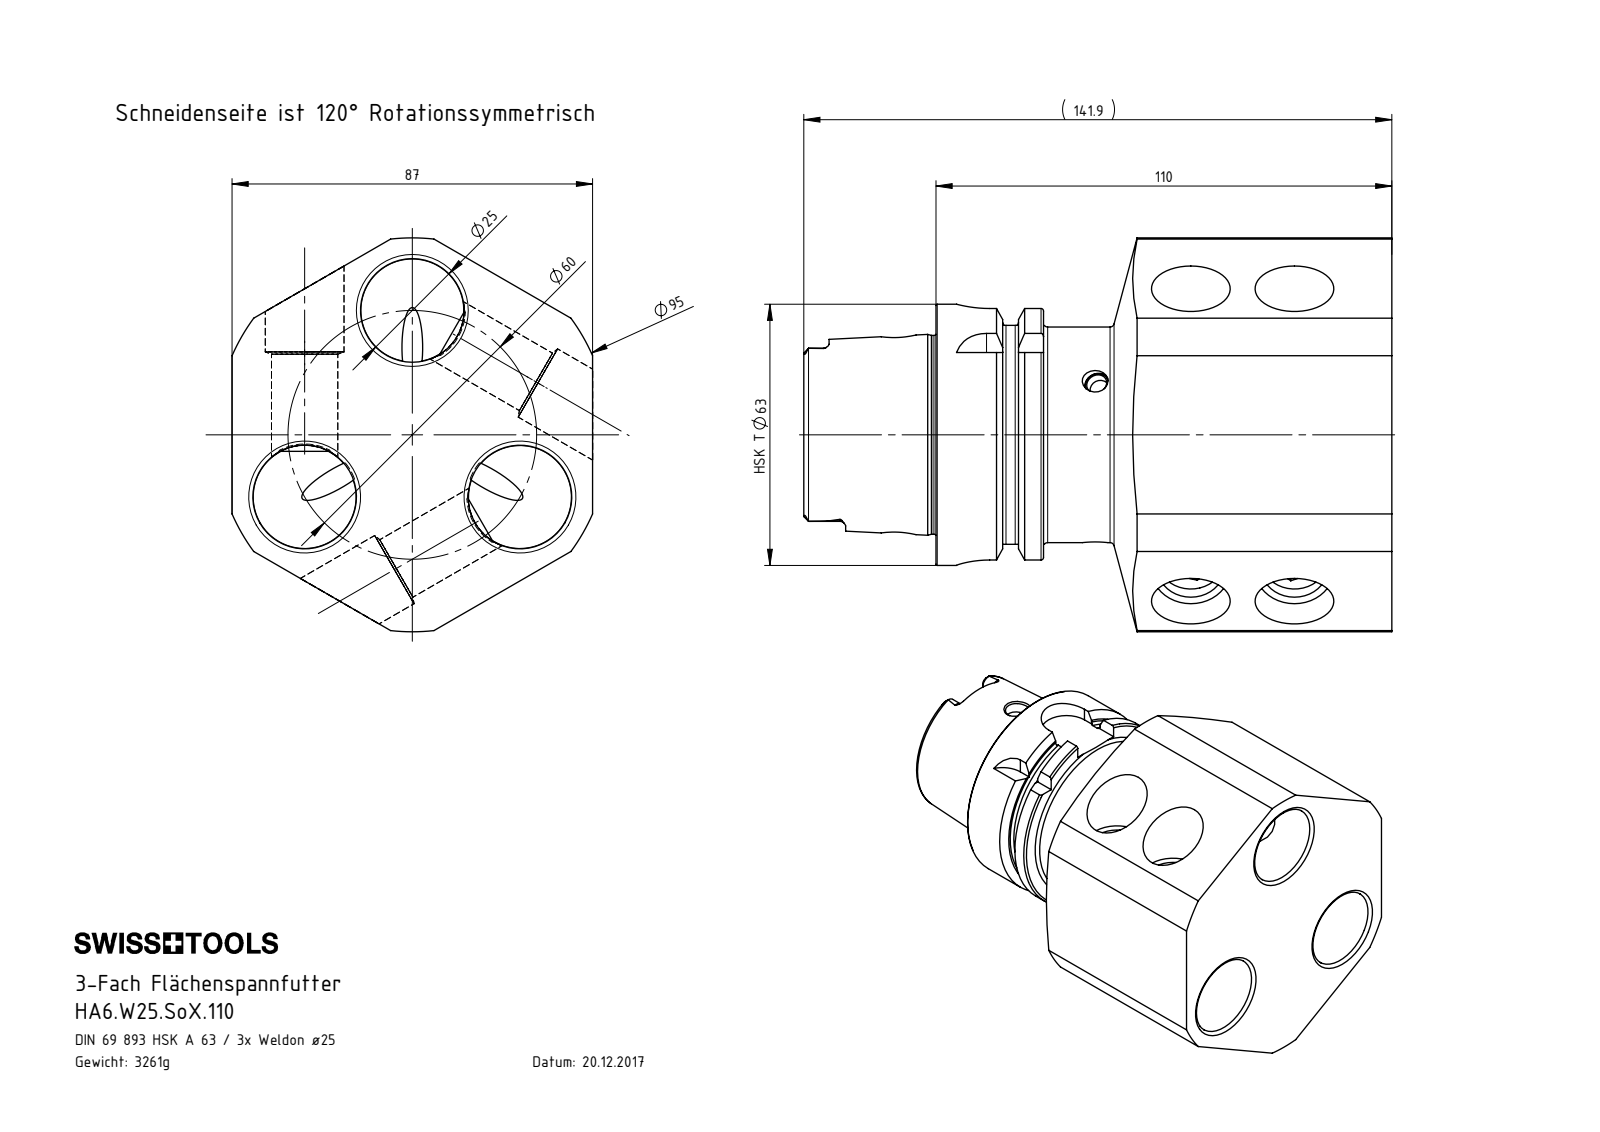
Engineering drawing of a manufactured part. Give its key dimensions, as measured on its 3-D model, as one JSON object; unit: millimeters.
{"part_name": "HA6-W25.SoX.110; W25-ER1.001.020; HA6-W25.SoX.110_A_Fertigbearbeitung; KVT_MB_600_060", "step_written_by": "SolidWorks 2017 (AUTOMOTIVE_DESIGN)", "units": "millimeters", "bodies": {"solids": 13, "faces": 529, "planar": 146, "cylindrical": 138, "other": 245}, "overall_size": [141.9, 95, 87], "volume_mm3": 415429, "surface_area_mm2": 90613, "round_holes": [[19, 7], [5, 6], [16, 6], [6, 3], [25, 3], [25.6, 3], [7.5, 1], [8.5, 1], [10, 1], [17, 1], [34, 1], [40, 1]], "round_bosses_or_shafts": [[18, 6], [6, 3], [63, 1], [54.95, 1], [52, 1], [47.94, 1]], "partial_cylinders_radius": [[1.4, 6], [2.88, 4], [8, 4], [47.5, 1]], "face_to_face_distances": [87, 59, 51, 110, 10, 25.95, 25.05, 84.05, 16, 9.95], "hole_center_spacings": [25, 30, 51.96, 75.13, 98.97]}
